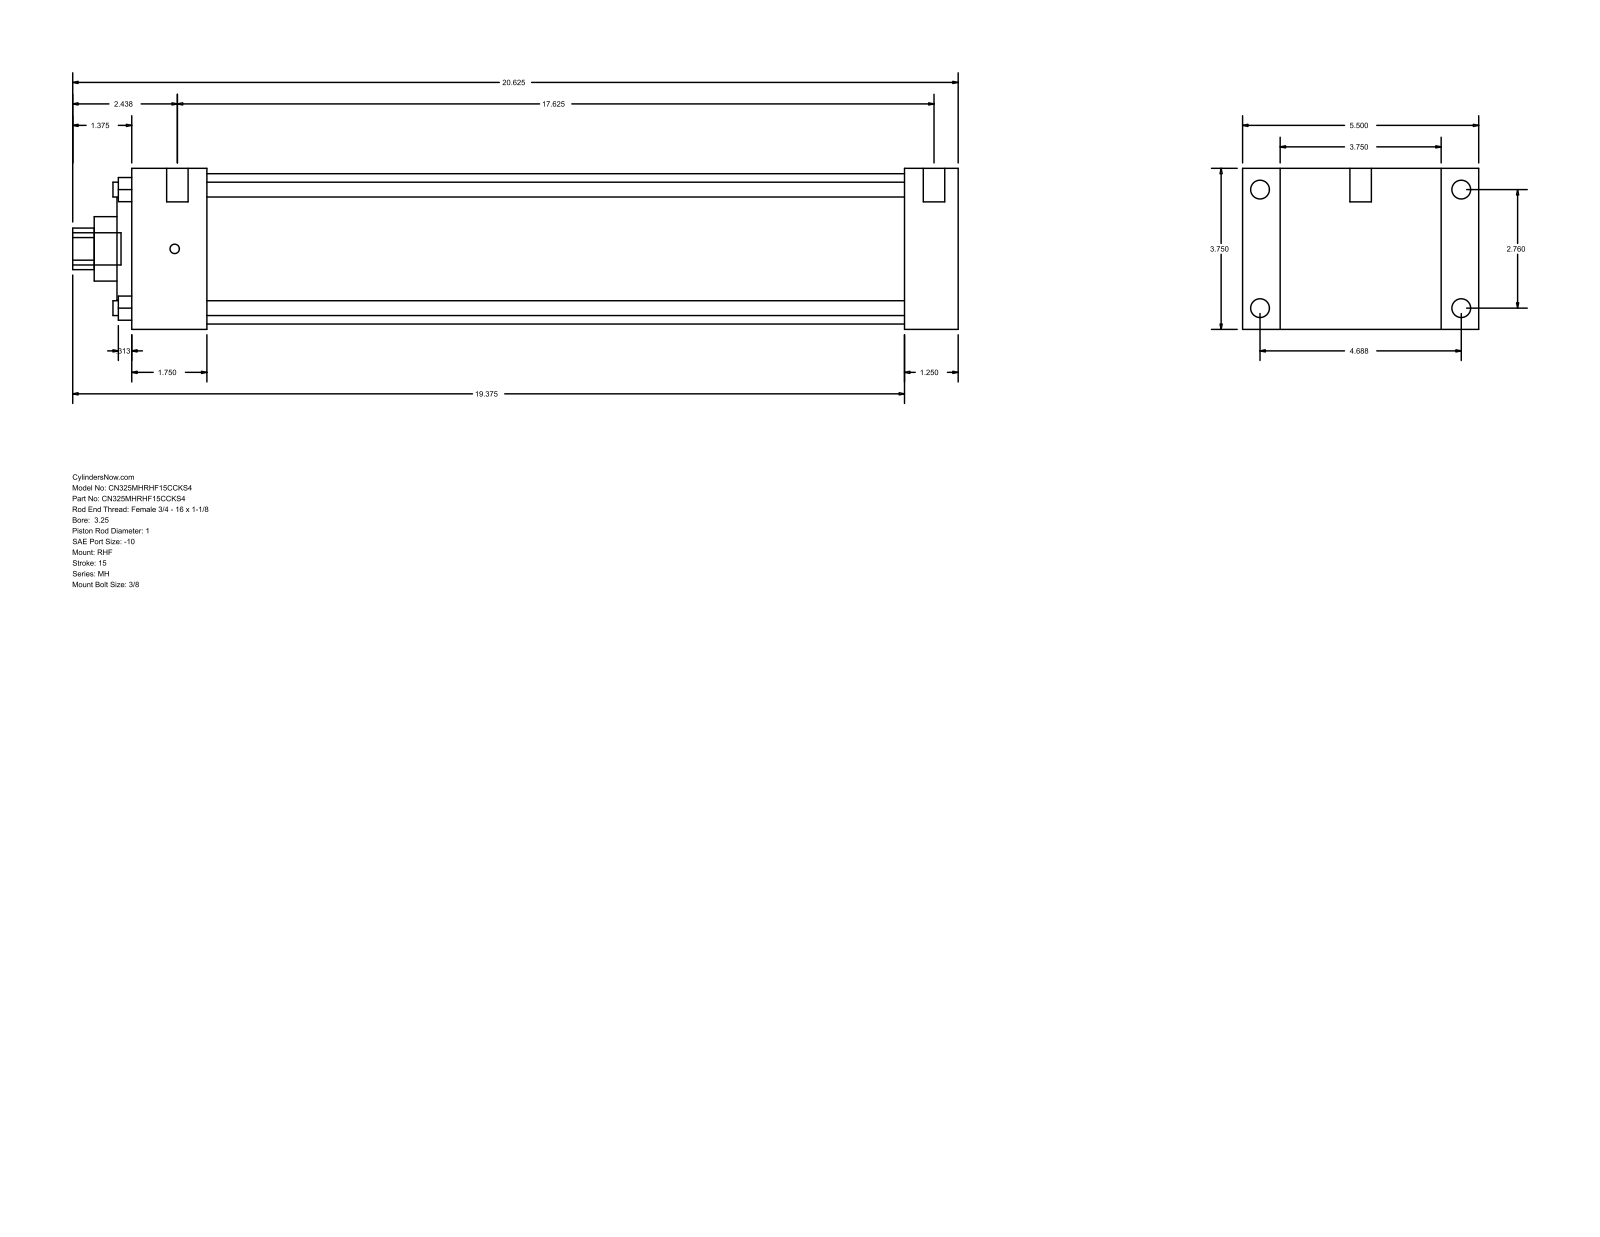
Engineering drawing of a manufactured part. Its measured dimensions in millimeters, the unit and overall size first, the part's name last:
Units: millimetres
Overall size (bounding box): 523.88 × 139.7 × 95.25
Round holes (diameter × count): ⌀8.76 ×4, ⌀25.4 ×1, ⌀38.1 ×1, ⌀60.33 ×1, ⌀88.9 ×1
Round bosses / shafts (diameter × count): ⌀11.13 ×4, ⌀5.56 ×4, ⌀12.7 ×2, ⌀19.05 ×1
Partial cylindrical surfaces — rounded edges, fillets, slot ends (radius × count): R12.29 ×1
Main face-to-face distances: 95.24, 31.76, 22.23, 117.47, 457.2, 488.96, 139.7, 44.46, 412.74, 444.5
Hole centre spacings: 49.57, 70.1, 99.14
Bodies: 0 solids, 90 faces (61 planar, 29 cylindrical, 0 other)
Part name (STEP PRODUCT): MH_RHF__0325_1
STEP written by: GSSL Pune (CONFIG_CONTROL_DESIGN)
